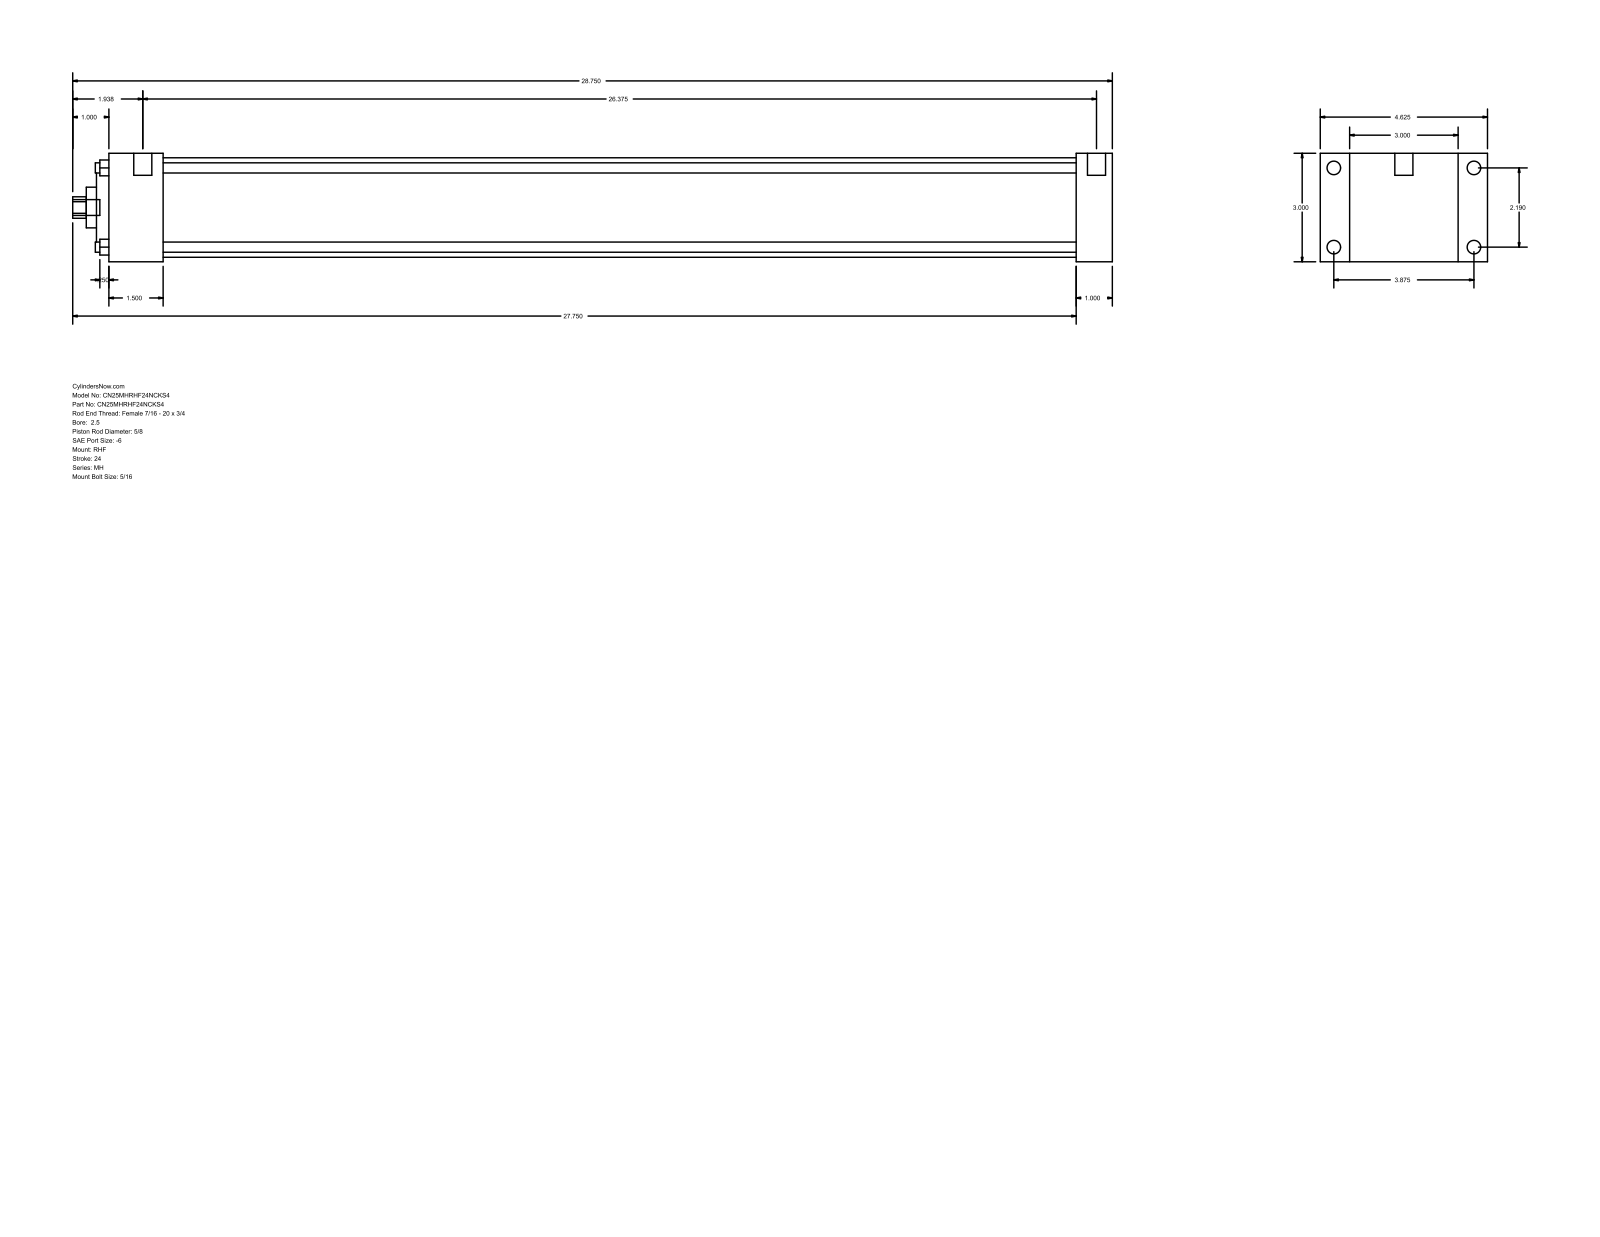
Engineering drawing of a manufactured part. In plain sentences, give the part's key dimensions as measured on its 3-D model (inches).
The part is named "MH_RHF__0250_0.625". Its 3-D file was written by "GSSL Pune (CONFIG_CONTROL_DESIGN)". It is 0 solids with 90 faces: 61 planar, 29 cylindrical and 0 other. Overall it measures 28.75 by 4.625 by 3 inches. Round holes: 4 of diameter 0.281, 1 of diameter 0.625, 1 of diameter 1.125, 1 of diameter 2.187, 1 of diameter 2.75. Round bosses or shafts: 4 of diameter 0.375, 4 of diameter 0.219, 2 of diameter 0.5, 1 of diameter 0.437. Partial cylindrical surfaces (rounded edges, fillets, slot ends): 1 of radius 0.297. The main face-to-face distances are 3, 1, 0.813, 3.813, 27.75, 26.75, 4.625, 1.5, 25.25, 26.25. The hole center spacings are 1.548, 2.19, 3.097.
